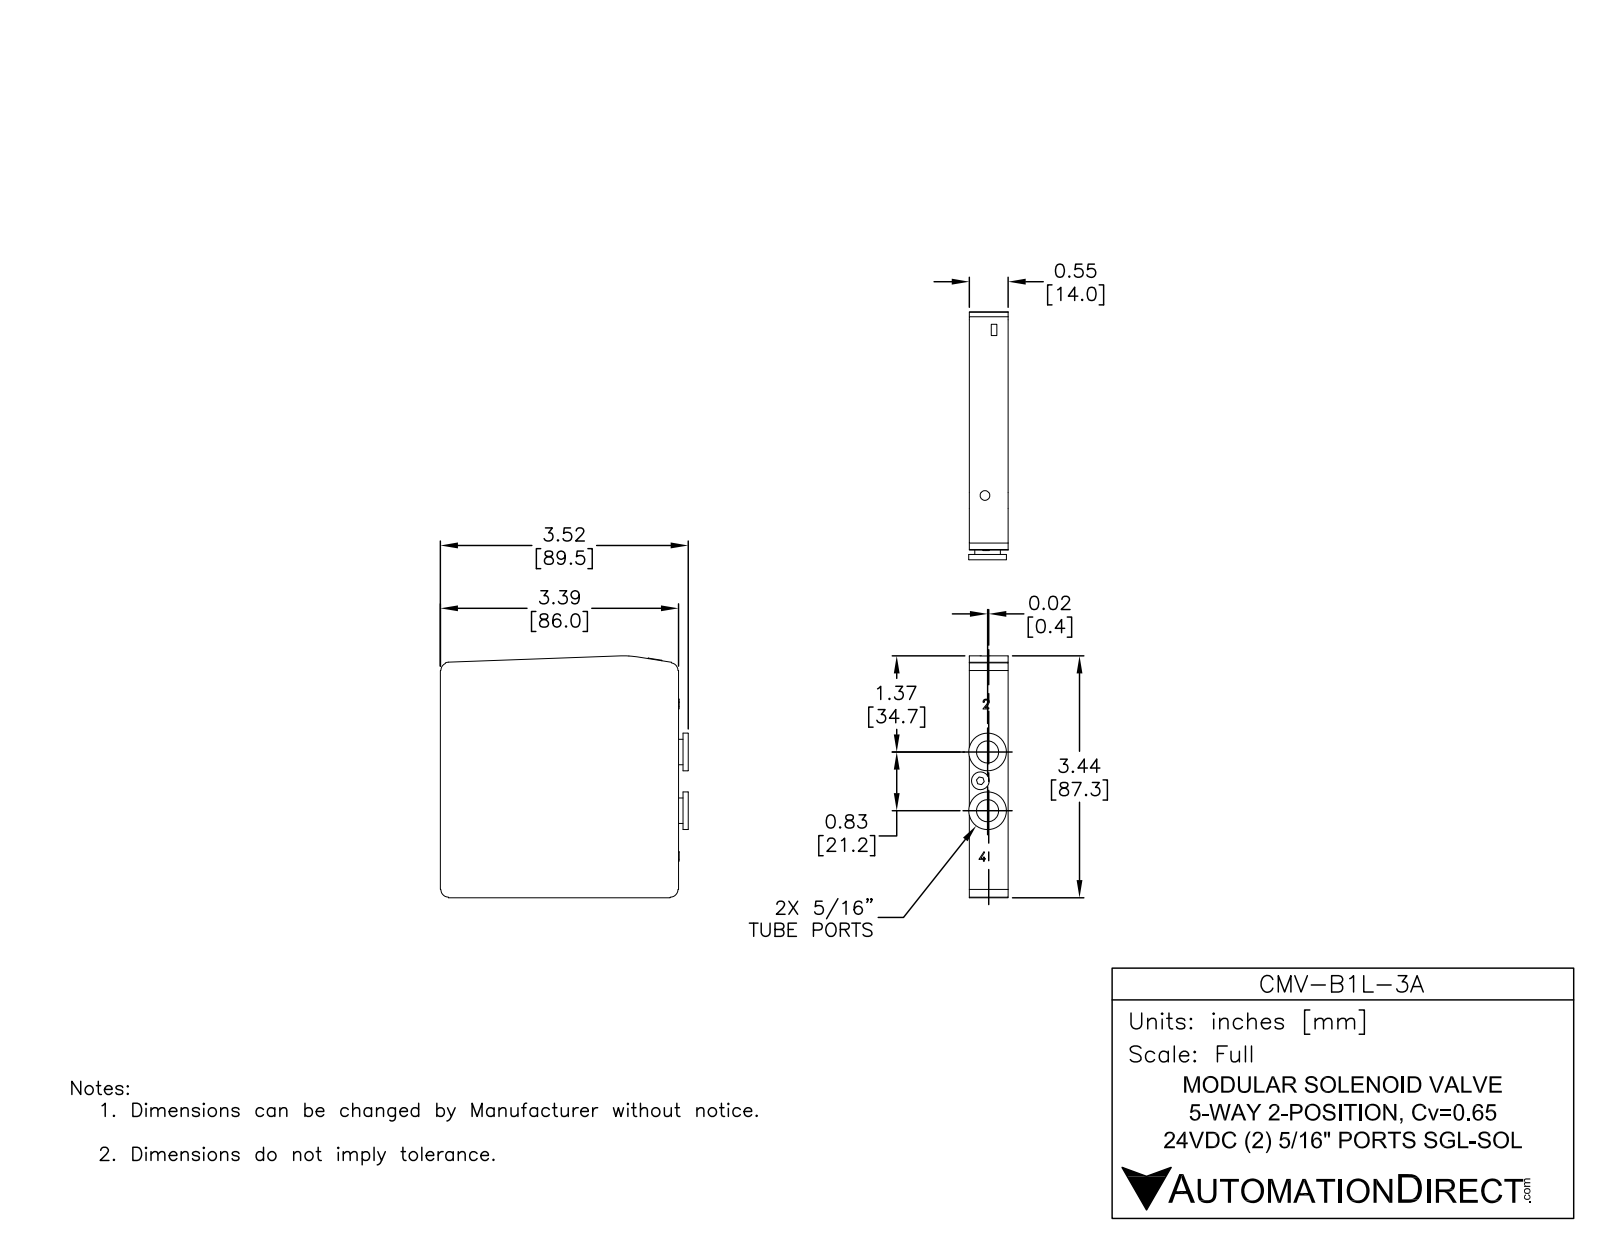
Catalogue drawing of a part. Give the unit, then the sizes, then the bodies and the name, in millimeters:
Units: millimetres
Overall size (bounding box): 89.5 × 87.3 × 21.68
Round holes (diameter × count): ⌀5.25 ×4, ⌀4.4 ×2, ⌀6.5 ×2, ⌀8 ×2, ⌀9.8 ×2, ⌀11.5 ×2, ⌀3.35 ×1, ⌀3.6 ×1, ⌀4.5 ×1, ⌀6.25 ×1, ⌀6.4 ×1
Round bosses / shafts (diameter × count): ⌀1.5 ×4, ⌀13.6 ×2, ⌀9.2 ×2, ⌀6.25 ×2, ⌀5.75 ×2, ⌀4.2 ×2, ⌀4 ×2, ⌀3.5 ×1
Partial cylindrical surfaces — rounded edges, fillets, slot ends (radius × count): R2.35 ×12, R0.78 ×4, R1.5 ×4, R2.8 ×4, R1 ×2, R0.15 ×1, R0.17 ×1, R0.25 ×1
Main face-to-face distances: 14, 4, 10, 12.75, 1.25, 2.75, 3, 1, 83, 3.75
Hole centre spacings: 9.7, 20.2, 22.17, 8.82, 9.6, 10.61, 10.63, 11.02
Volume: 95 672 mm³ · Surface area: 47 922 mm²
Bodies: 77 solids, 1131 faces (865 planar, 157 cylindrical, 109 other)
Part name (STEP PRODUCT): CMV-B1L-3A
STEP written by: SolidWorks 2013 (AUTOMOTIVE_DESIGN)
